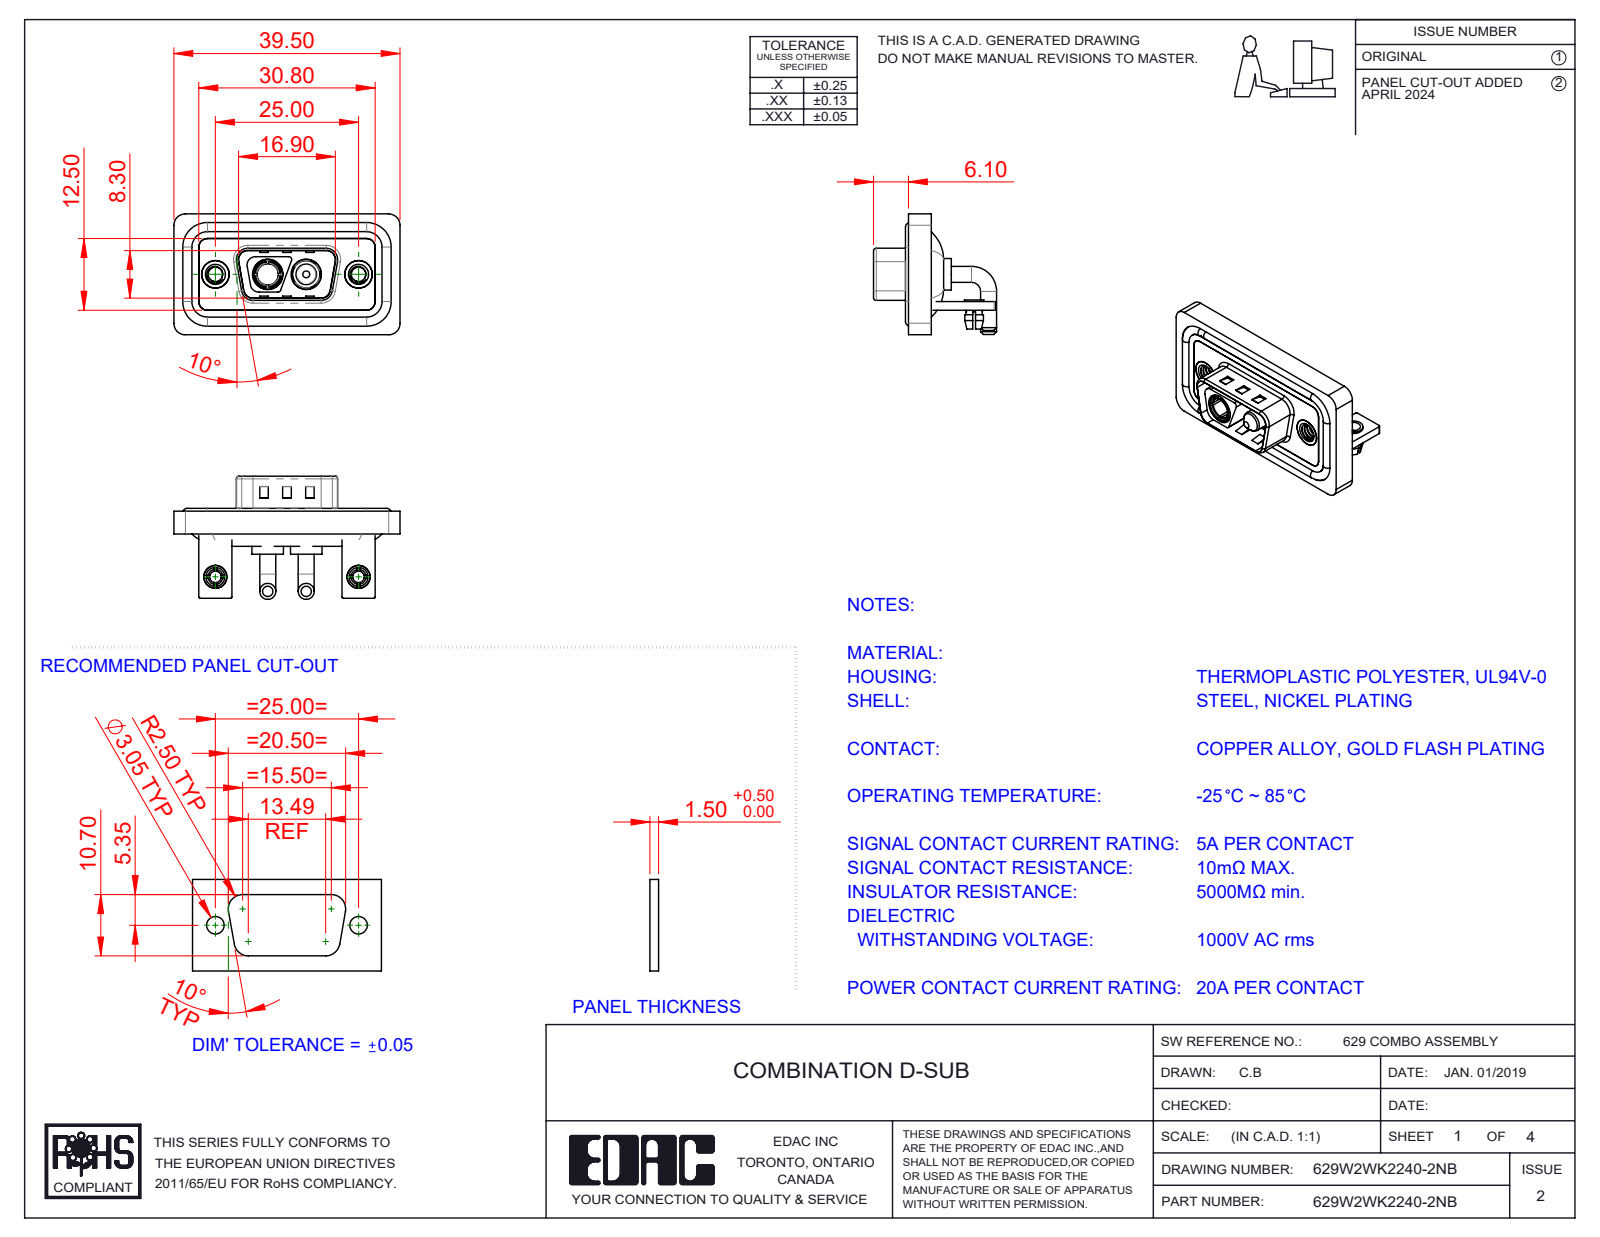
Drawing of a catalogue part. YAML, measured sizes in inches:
part_name: "Power Pin_20A RA; 629Combo Shell Rear_09 Contacts; 629Combo Threaded Rivet_B; 629Combo Shell Front_09 Contacts (+6 more)"
step_written_by: "SolidWorks 2023 (CONFIG_CONTROL_DESIGN)"
units: inches
bodies: {solids: 15, faces: 672, planar: 257, cylindrical: 281, other: 134}
overall_size: [1.555, 0.846, 0.831]
volume: 0.305
surface_area: 12.91
round_holes:
  - {diameter: 0.098, count: 4}
  - {diameter: 0.079, count: 2}
  - {diameter: 0.126, count: 2}
  - {diameter: 0.157, count: 2}
  - {diameter: 0.189, count: 2}
  - {diameter: 0.191, count: 2}
  - {diameter: 0.197, count: 2}
  - {diameter: 0.209, count: 2}
  - {diameter: 0.146, count: 1}
round_bosses_or_shafts:
  - {diameter: 0.11, count: 4}
  - {diameter: 0.063, count: 4}
  - {diameter: 0.217, count: 2}
  - {diameter: 0.205, count: 2}
  - {diameter: 0.193, count: 2}
  - {diameter: 0.187, count: 2}
  - {diameter: 0.157, count: 2}
  - {diameter: 0.148, count: 2}
partial_cylinders:
  - {radius: 0.059, count: 20}
  - {radius: 0.079, count: 19}
  - {radius: 0.01, count: 16}
  - {radius: 0.02, count: 11}
  - {radius: 0.063, count: 8}
  - {radius: 0.024, count: 4}
  - {radius: 0.026, count: 4}
  - {radius: 0.035, count: 4}
face_to_face_distances: [0.016, 0.059, 0.114, 0.031, 0.043, 0.047, 0.083, 0.063, 0.146, 0.098]
hole_center_spacings: [0.36, 0.624, 0.984, 0.265]
